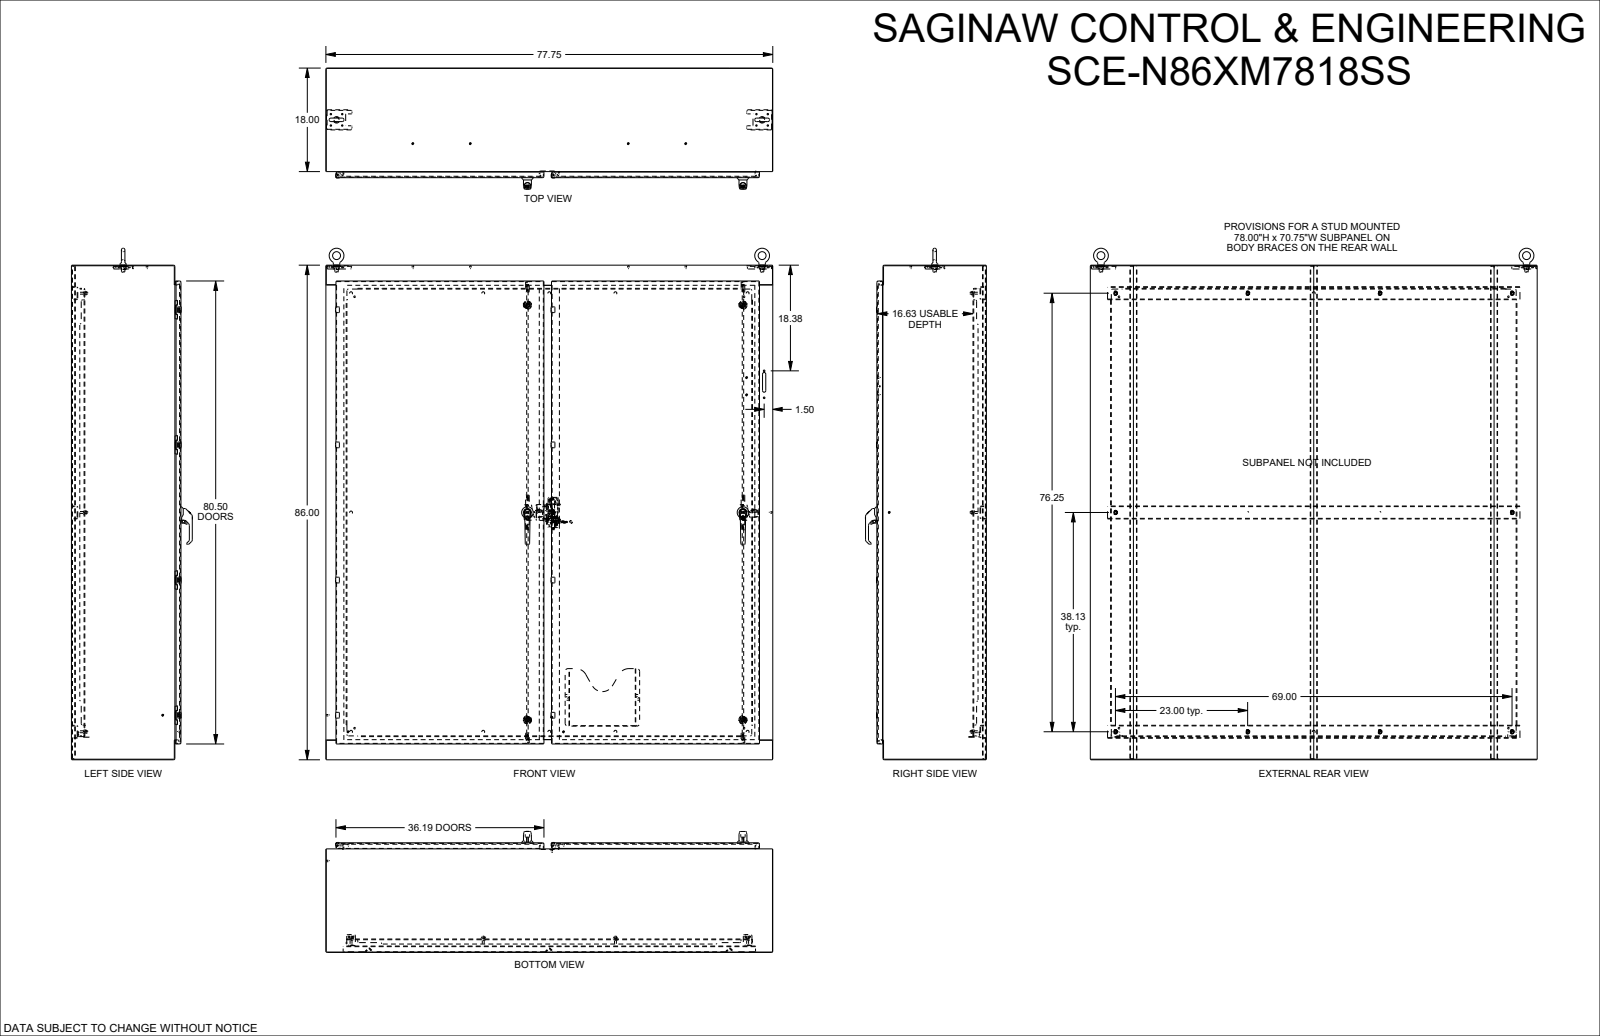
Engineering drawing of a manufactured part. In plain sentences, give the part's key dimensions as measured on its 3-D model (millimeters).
The part is named "SCE-N86XM7818". Its 3-D file was written by "SolidWorks 2023 (AUTOMOTIVE_DESIGN)". It is 47 solids with 7397 faces: 3076 planar, 2489 cylindrical and 1832 other. Overall it measures 2259.2 by 1974.9 by 534.6 millimeters. Its volume is 38 980 000 cubic millimeters and its surface area 29 270 000 square millimeters. Round holes: 16 of diameter 5.2, 16 of diameter 6.2, 14 of diameter 6.4, 8 of diameter 1, 8 of diameter 4.3, 8 of diameter 5.5, 8 of diameter 9.5, 8 of diameter 9.5, 4 of diameter 2.9, 4 of diameter 5.1, 4 of diameter 6.5, 4 of diameter 8.7. Round bosses or shafts: 24 of diameter 4.3, 19 of diameter 6.4, 16 of diameter 6.1, 10 of diameter 5, 4 of diameter 35.6, 4 of diameter 8.7, 2 of diameter 51, 2 of diameter 29.8. Partial cylindrical surfaces (rounded edges, fillets, slot ends): 211 of radius 0.8, 162 of radius 0.4, 66 of radius 3.2, 65 of radius 0.5, 59 of radius 1, 48 of radius 0.5, 43 of radius 6.4, 42 of radius 1. The main face-to-face distances are 2.6, 481.4, 478.8, 484.1, 454.6, 26.9, 1972.2, 2181.8, 451.9, 29.5. The hole center spacings are 596.9, 1193.8, 952.5, 899.9, 96.4, 953.7, 1010.8, 1790.7.
